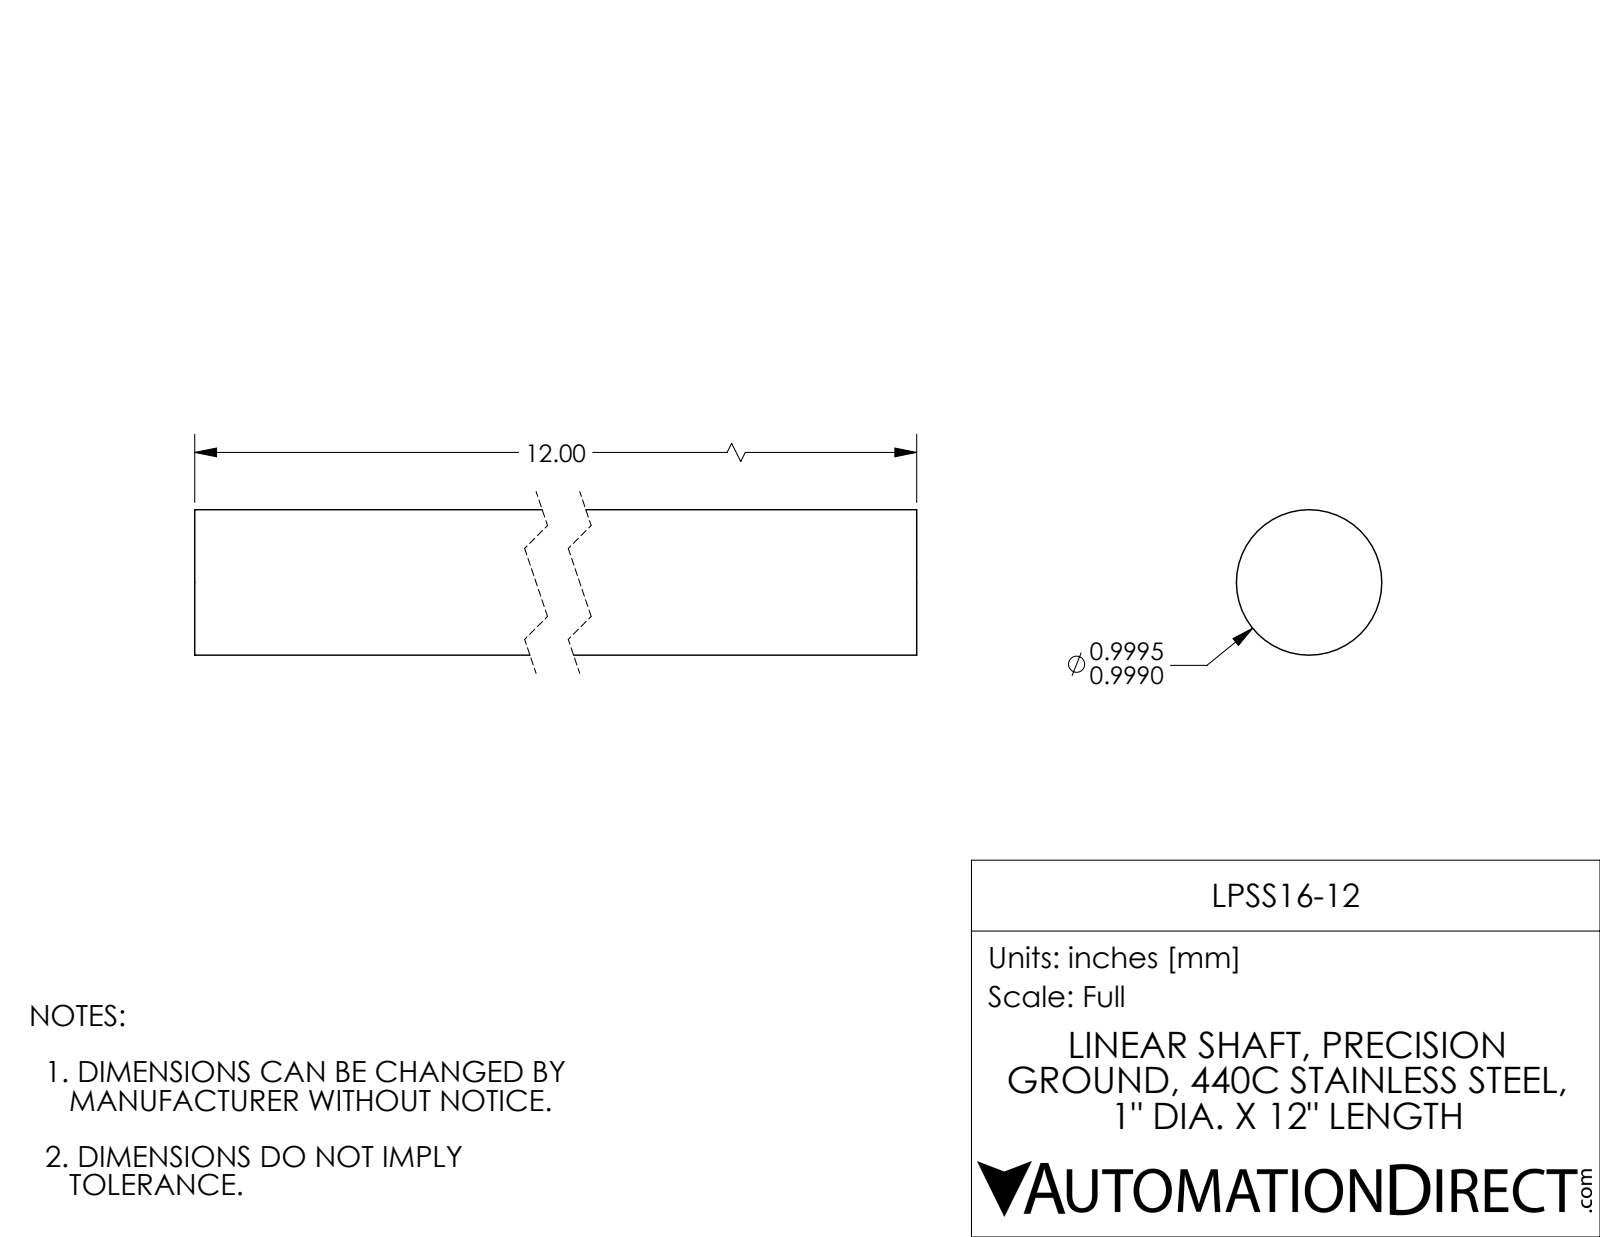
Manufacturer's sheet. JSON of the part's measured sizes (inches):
{"part_name": "LPSS16-12", "step_written_by": "SolidWorks 2017 (AUTOMOTIVE_DESIGN)", "units": "inches", "bodies": {"solids": 1, "faces": 4, "planar": 2, "cylindrical": 2, "other": 0}, "overall_size": [12, 0.999, 0.999], "volume_in3": 9.415, "surface_area_in2": 39.25, "round_bosses_or_shafts": [[1, 1]], "face_to_face_distances": [12]}
